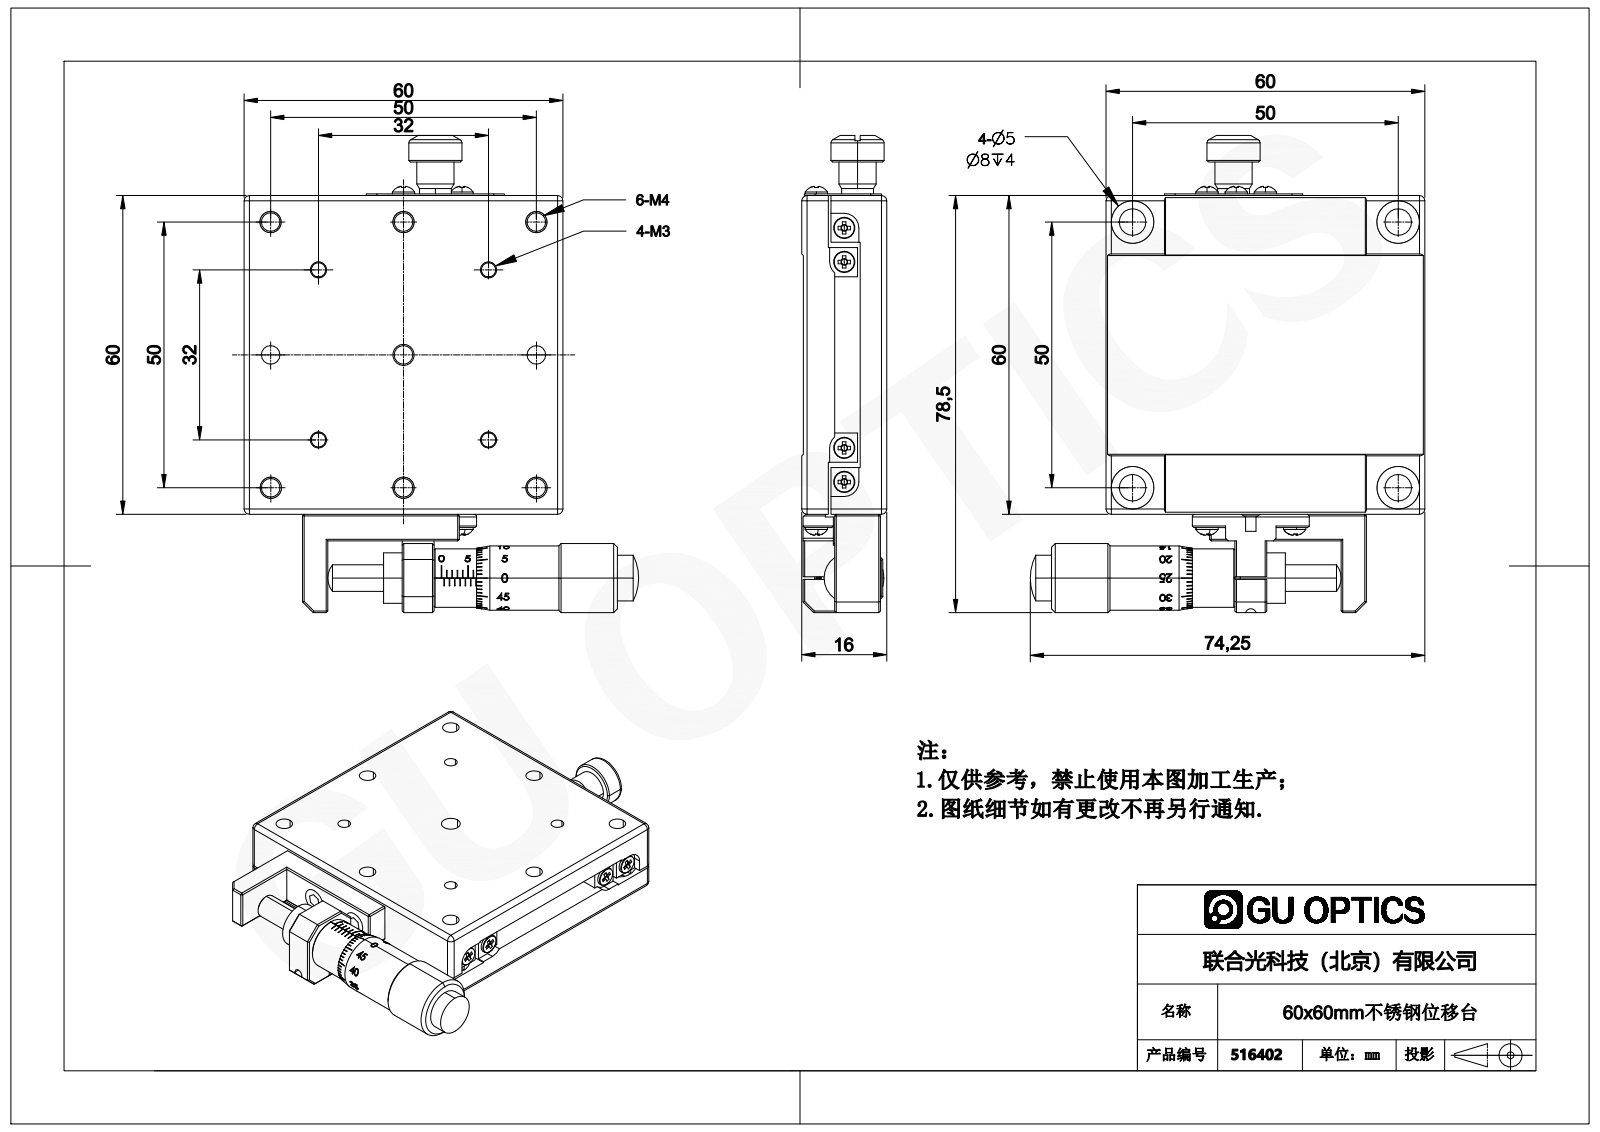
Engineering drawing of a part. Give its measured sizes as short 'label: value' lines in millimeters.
name: MX60-SS
written by: SolidWorks 2020 (CONFIG_CONTROL_DESIGN)
unit: mm
bodies: 14 solids, 1668 faces (799 planar, 331 cylindrical, 538 other)
size: 89.8 × 74.25 × 16
volume: 53 402 mm³; area: 26 270 mm²
holes: 12× ⌀3.5, 5× ⌀5, 4× ⌀2.7, 4× ⌀8, 2× ⌀3, 1× ⌀2.05, 1× ⌀2.9, 1× ⌀4, 1× ⌀9.5, 1× ⌀11
bosses: 4× ⌀4.2, 4× ⌀4, 4× ⌀2.5, 2× ⌀2, 1× ⌀13, 1× ⌀12.1, 1× ⌀10, 1× ⌀9.2
rounds: 12× R1, 4× R2, 4× R2.75, 2× R1.65, 1× R5.49, 1× R6.04
face distances: 5, 5.5, 4.8, 9.8, 15.7, 10.7, 5.9, 6, 0.5, 11
hole spacings: 25, 18.36, 35.36, 41.98, 44.01, 55.9, 50, 12.73
